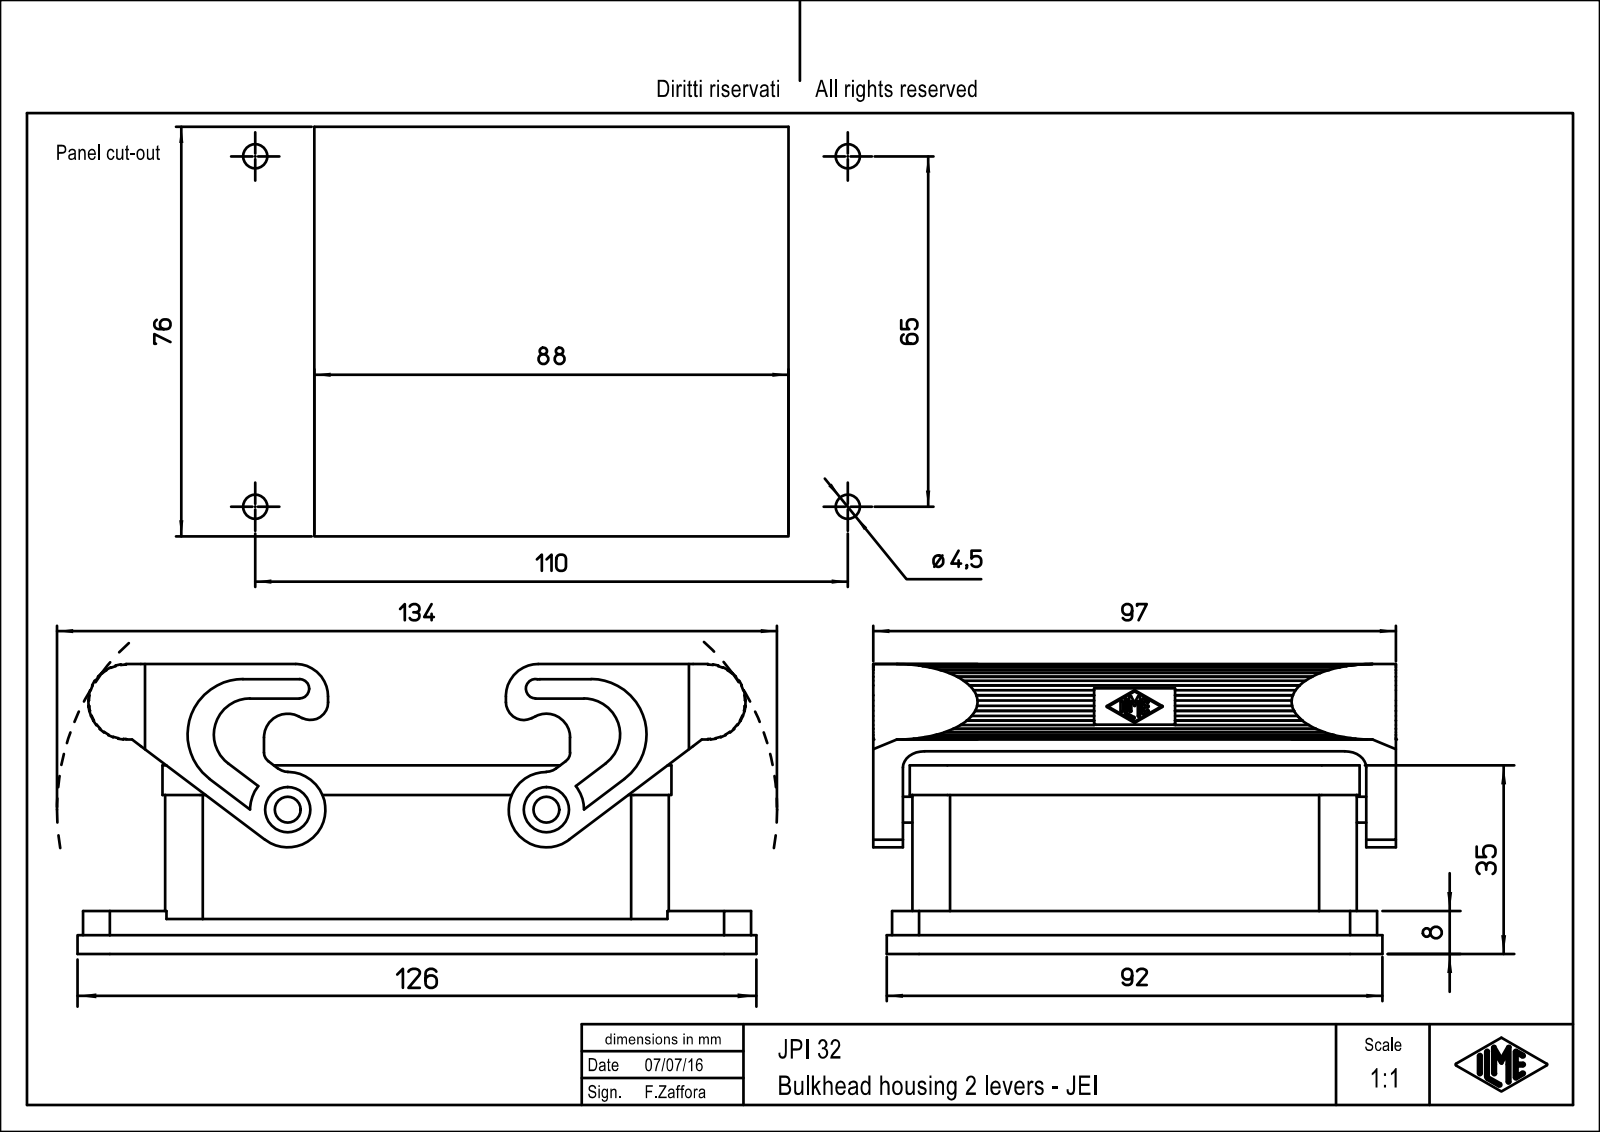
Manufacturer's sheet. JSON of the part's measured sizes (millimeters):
{"part_name": "JPI_32", "step_written_by": "PTC Creo Elements/Direct Modeling 19.0B 21-Mar-2015 (C) Parametric Technology GmbH (AUTOMOTIVE_DESIGN)", "units": "millimeters", "bodies": {"solids": 1, "faces": 542, "planar": 278, "cylindrical": 256, "other": 8}, "overall_size": [126, 97, 53.8], "volume_mm3": 107849, "surface_area_mm2": 56361, "round_holes": [[3, 8], [4.5, 4], [6.8, 2], [8.4, 2]], "round_bosses_or_shafts": [[0.4, 4], [4.8, 2]], "partial_cylinders_radius": [[0.2, 18], [3, 14], [7, 8], [6, 6], [2.5, 4], [4, 4], [5, 4], [0.1, 3]], "face_to_face_distances": [3.5, 79, 86.25, 90, 7.25, 1.75, 5.25, 80.75, 84.25, 89.75], "hole_center_spacings": [16.32, 27, 32.81, 35, 39.95, 65.55, 77.5, 82.07]}
